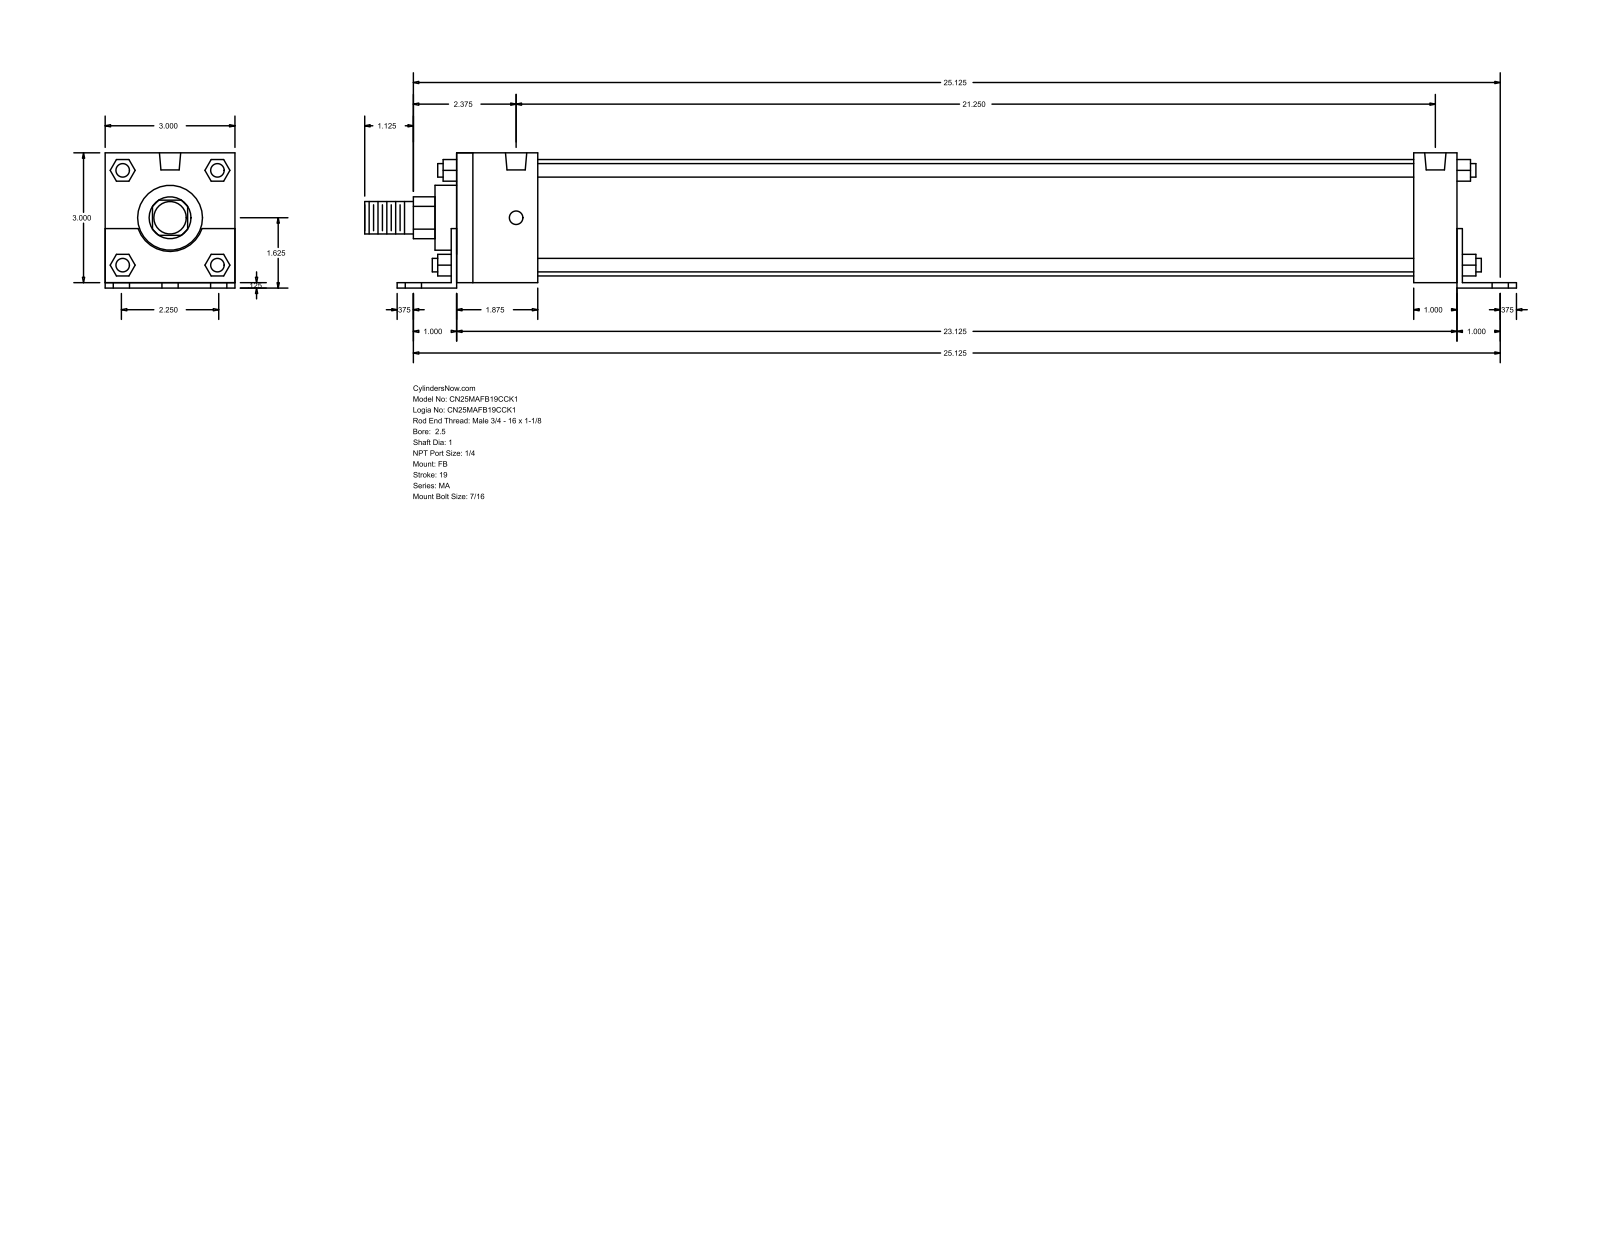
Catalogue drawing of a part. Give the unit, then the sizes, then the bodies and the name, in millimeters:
Units: millimetres
Overall size (bounding box): 676.27 × 79.38 × 76.2
Round holes (diameter × count): ⌀11.11 ×6, ⌀7.94 ×4, ⌀12.49 ×2
Round bosses / shafts (diameter × count): ⌀7.94 ×4, ⌀68.33 ×1, ⌀38.1 ×1, ⌀25.4 ×1, ⌀19.05 ×1
Partial cylindrical surfaces — rounded edges, fillets, slot ends (radius × count): R12.29 ×1, R19.81 ×1
Main face-to-face distances: 76.2, 3.17, 79.37, 587.37, 3.18, 12.7, 590.55, 28.57, 50.8, 47.63
Hole centre spacings: 28.57, 638.81, 638.17, 47.61, 57.14, 66.75, 539.75, 578.55
Bodies: 0 solids, 140 faces (105 planar, 35 cylindrical, 0 other)
Part name (STEP PRODUCT): MA_FB__0250_1
STEP written by: GSSL Pune (CONFIG_CONTROL_DESIGN)
